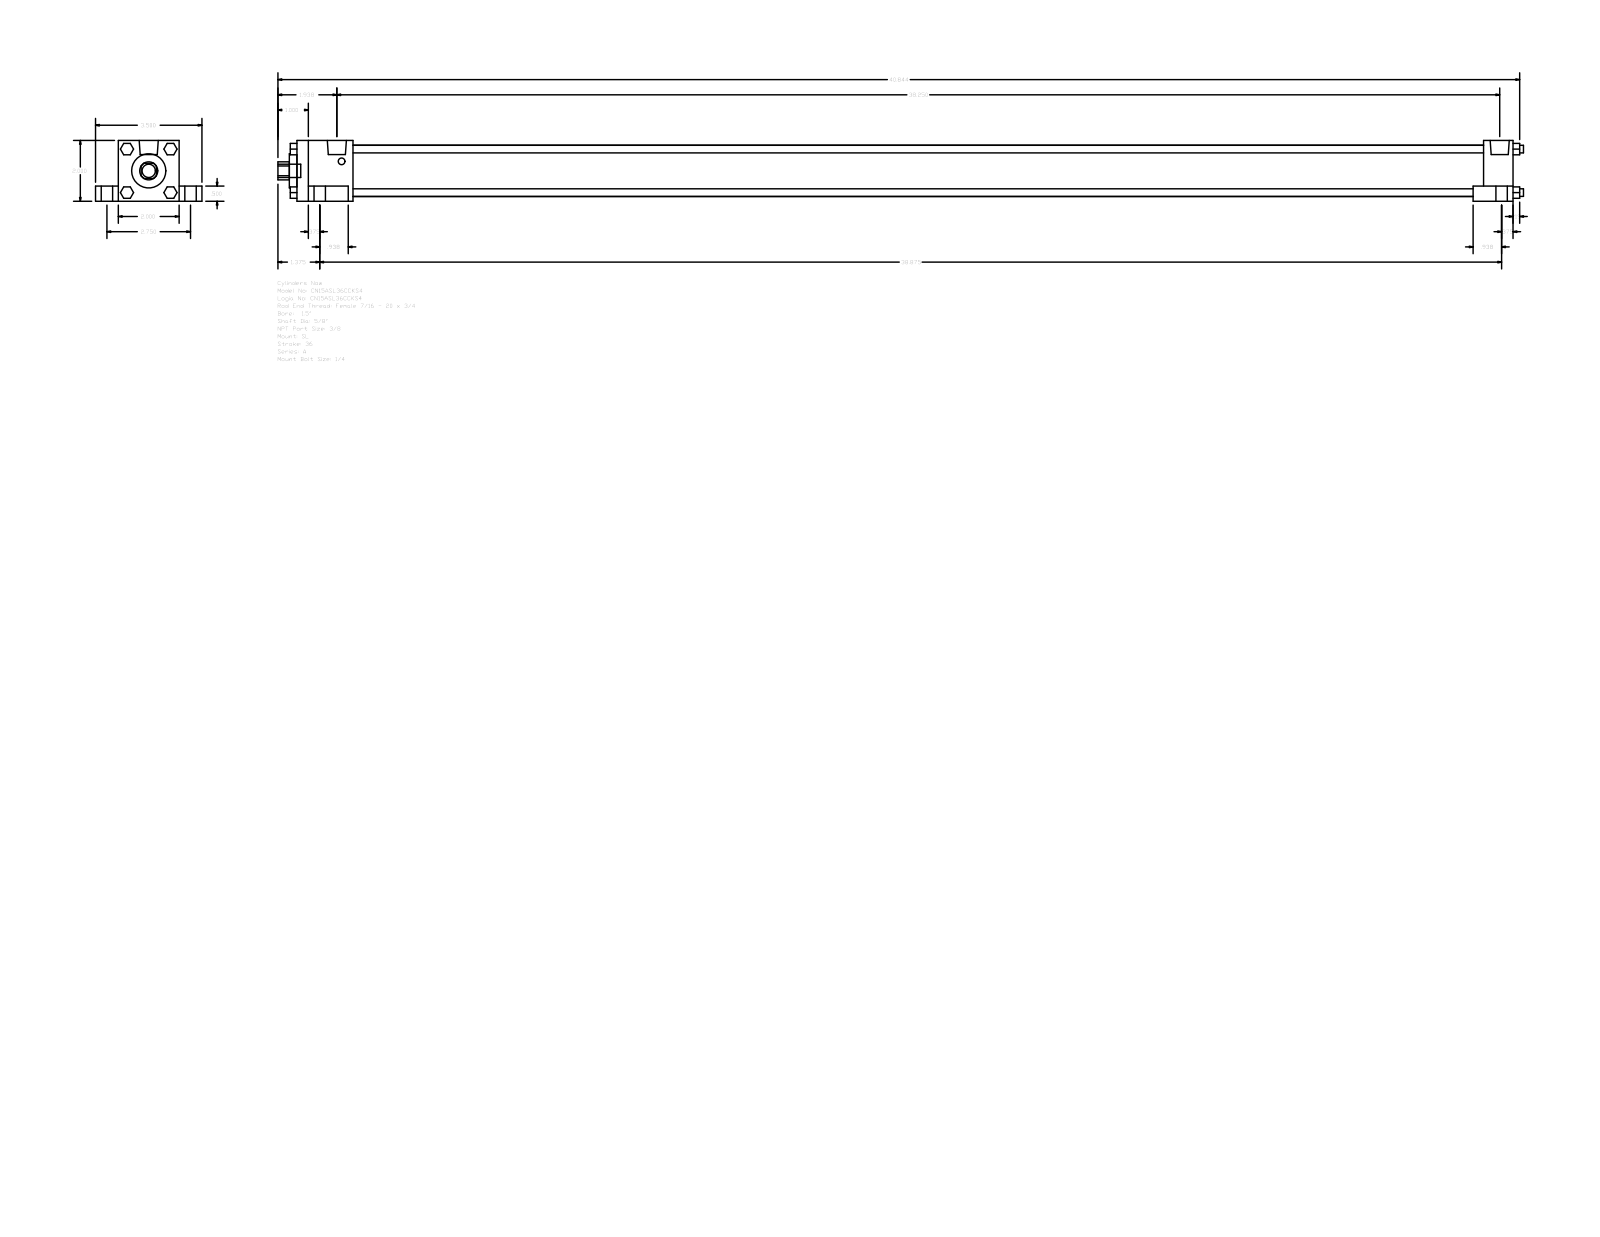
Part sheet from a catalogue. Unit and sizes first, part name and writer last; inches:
Units: inches
Overall size (bounding box): 40.969 × 3.5 × 2
Round holes (diameter × count): ⌀0.625 ×1, ⌀1.125 ×1, ⌀1.69 ×1
Round bosses / shafts (diameter × count): ⌀0.625 ×4, ⌀0.375 ×4, ⌀0.25 ×4, ⌀0.219 ×4, ⌀0.627 ×2, ⌀0.437 ×1
Partial cylindrical surfaces — rounded edges, fillets, slot ends (radius × count): R0.297 ×1
Main face-to-face distances: 2, 0.75, 0.5, 1.5, 2.75, 40, 0.375, 1.313, 39.031, 0.969
Bodies: 0 solids, 148 faces (112 planar, 36 cylindrical, 0 other)
Part name (STEP PRODUCT): A_SL__0150_0.625
STEP written by: GSSL Pune (CONFIG_CONTROL_DESIGN)
